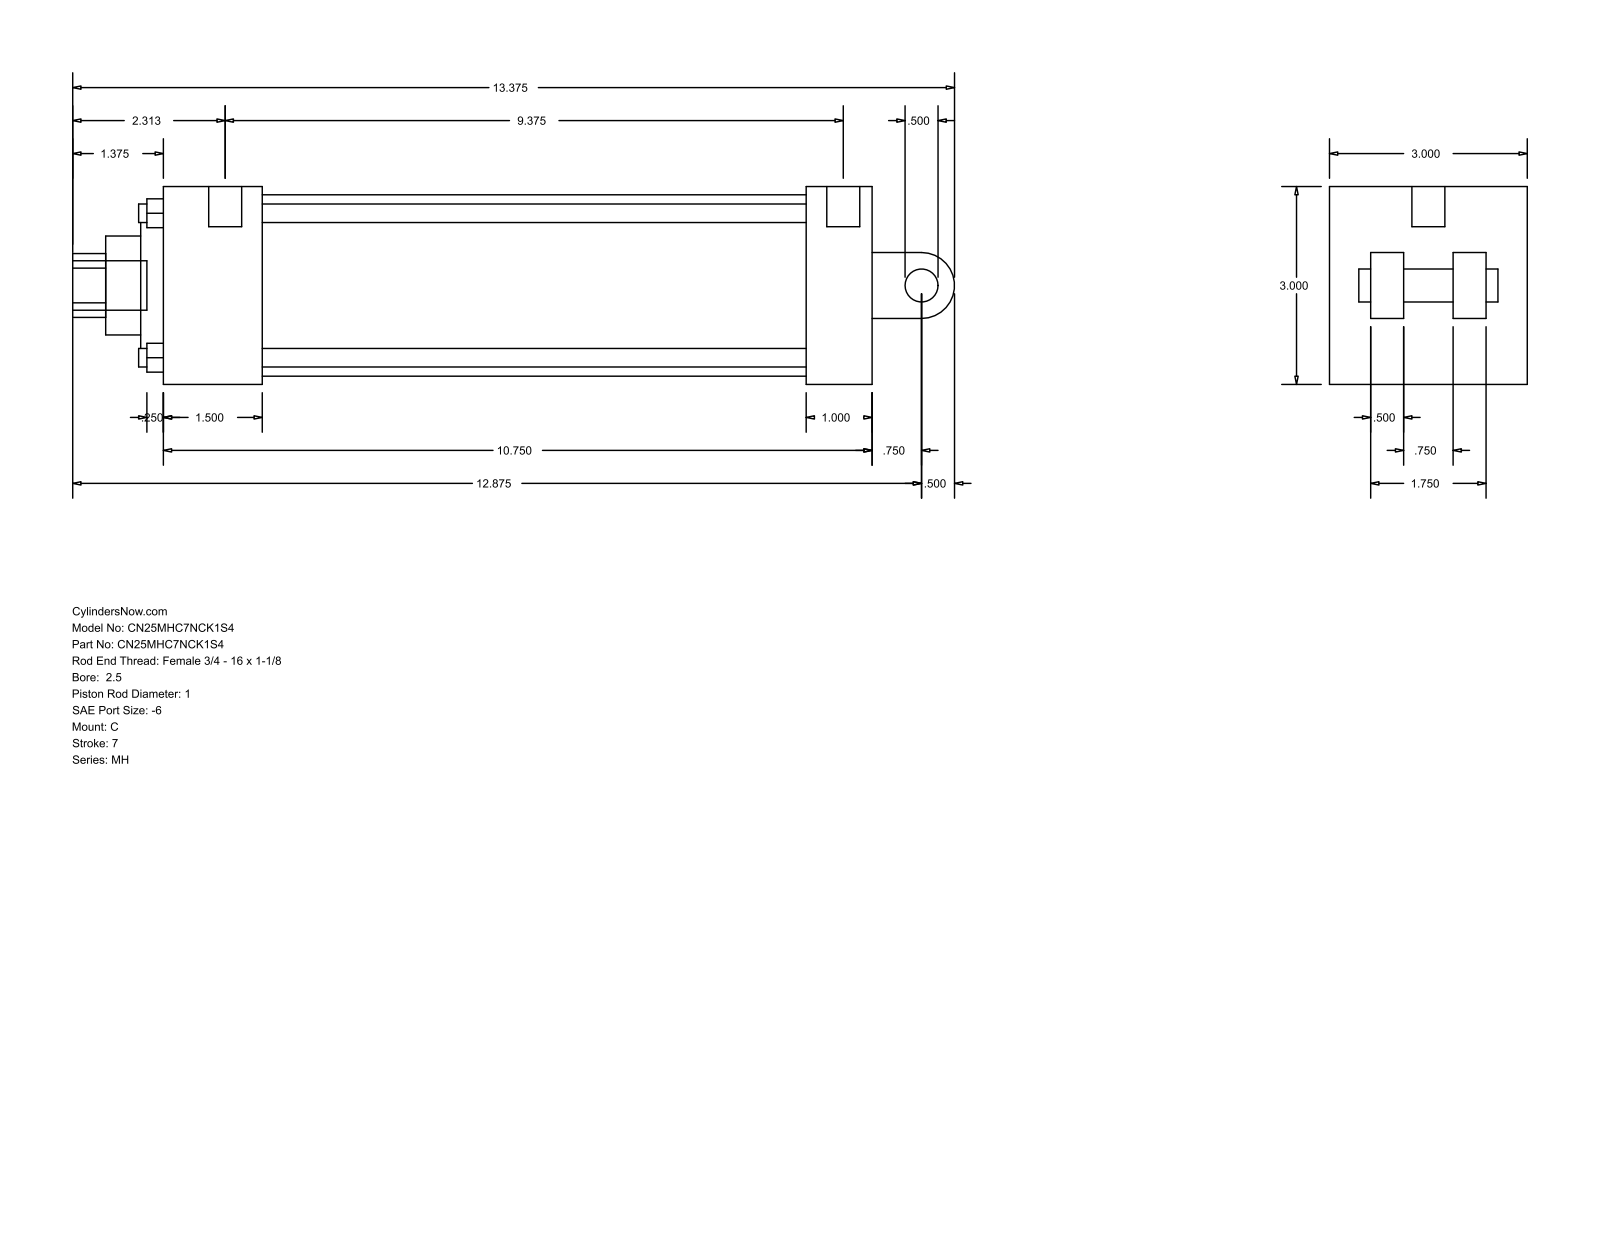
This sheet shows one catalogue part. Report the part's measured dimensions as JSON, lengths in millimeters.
{"part_name": "MH_C__0250_1", "step_written_by": "GSSL Pune (CONFIG_CONTROL_DESIGN)", "units": "millimeters", "bodies": {"solids": 0, "faces": 101, "planar": 71, "cylindrical": 30, "other": 0}, "overall_size": [339.73, 76.2, 76.2], "round_holes": [[7.14, 4], [5.56, 2], [12.7, 1], [25.4, 1], [38.1, 1], [60.33, 1], [69.85, 1]], "round_bosses_or_shafts": [[12.7, 2], [5.56, 2], [19.05, 1]], "partial_cylinders_radius": [[12.29, 1], [12.7, 1]], "face_to_face_distances": [76.2, 273.06, 15.87, 60.33, 247.65, 25.41, 38.11, 209.54, 234.95, 12.7], "hole_center_spacings": [39.33, 55.62, 78.66, 3.18]}
